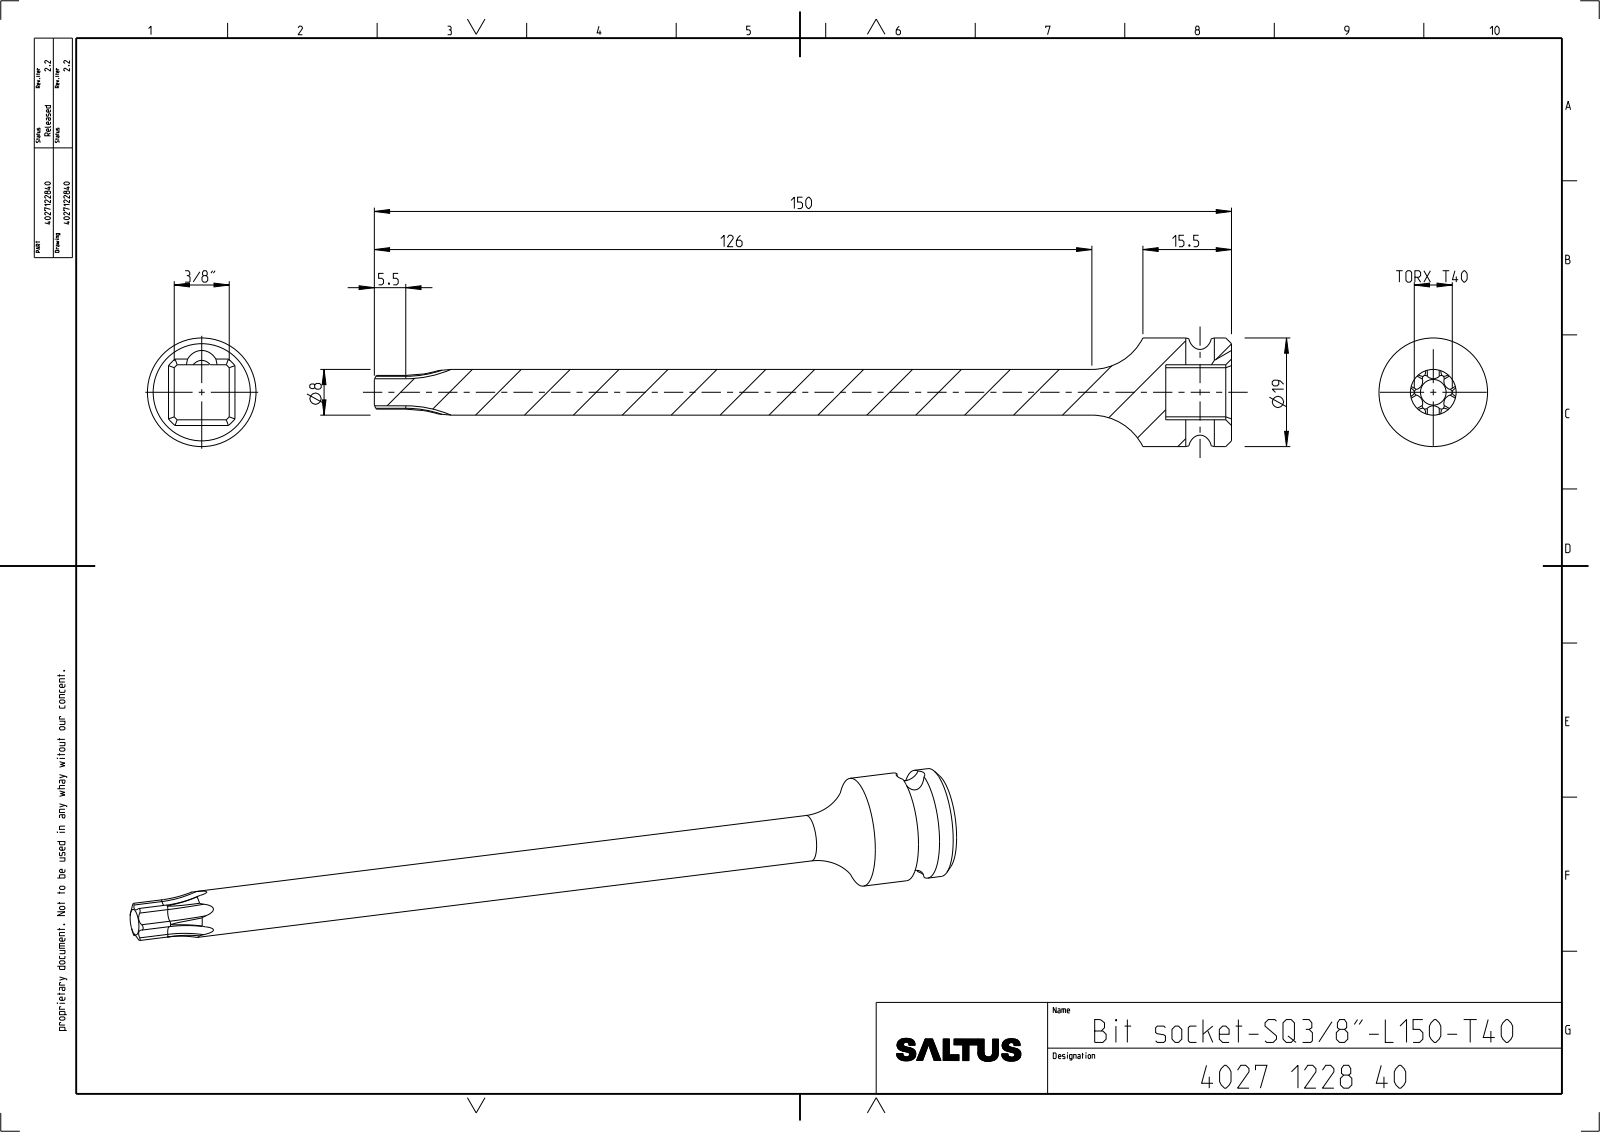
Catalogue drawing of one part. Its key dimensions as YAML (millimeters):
part_name: "4027122840"
step_written_by: "CREO PARAMETRIC BY PTC INC, 2022414 (CONFIG_CONTROL_DESIGN)"
units: millimeters
bodies: {solids: 1, faces: 81, planar: 12, cylindrical: 33, other: 36}
overall_size: [150, 19, 19]
volume: 9852
surface_area: 5230
round_holes:
  - {diameter: 5, count: 1}
round_bosses_or_shafts:
  - {diameter: 19, count: 1}
  - {diameter: 8, count: 1}
partial_cylinders:
  - {radius: 0.51, count: 6}
  - {radius: 1.47, count: 6}
  - {radius: 3, count: 1}
  - {radius: 3.33, count: 1}
  - {radius: 6.45, count: 1}
face_to_face_distances: [9.62, 11.5, 150, 138.5]
